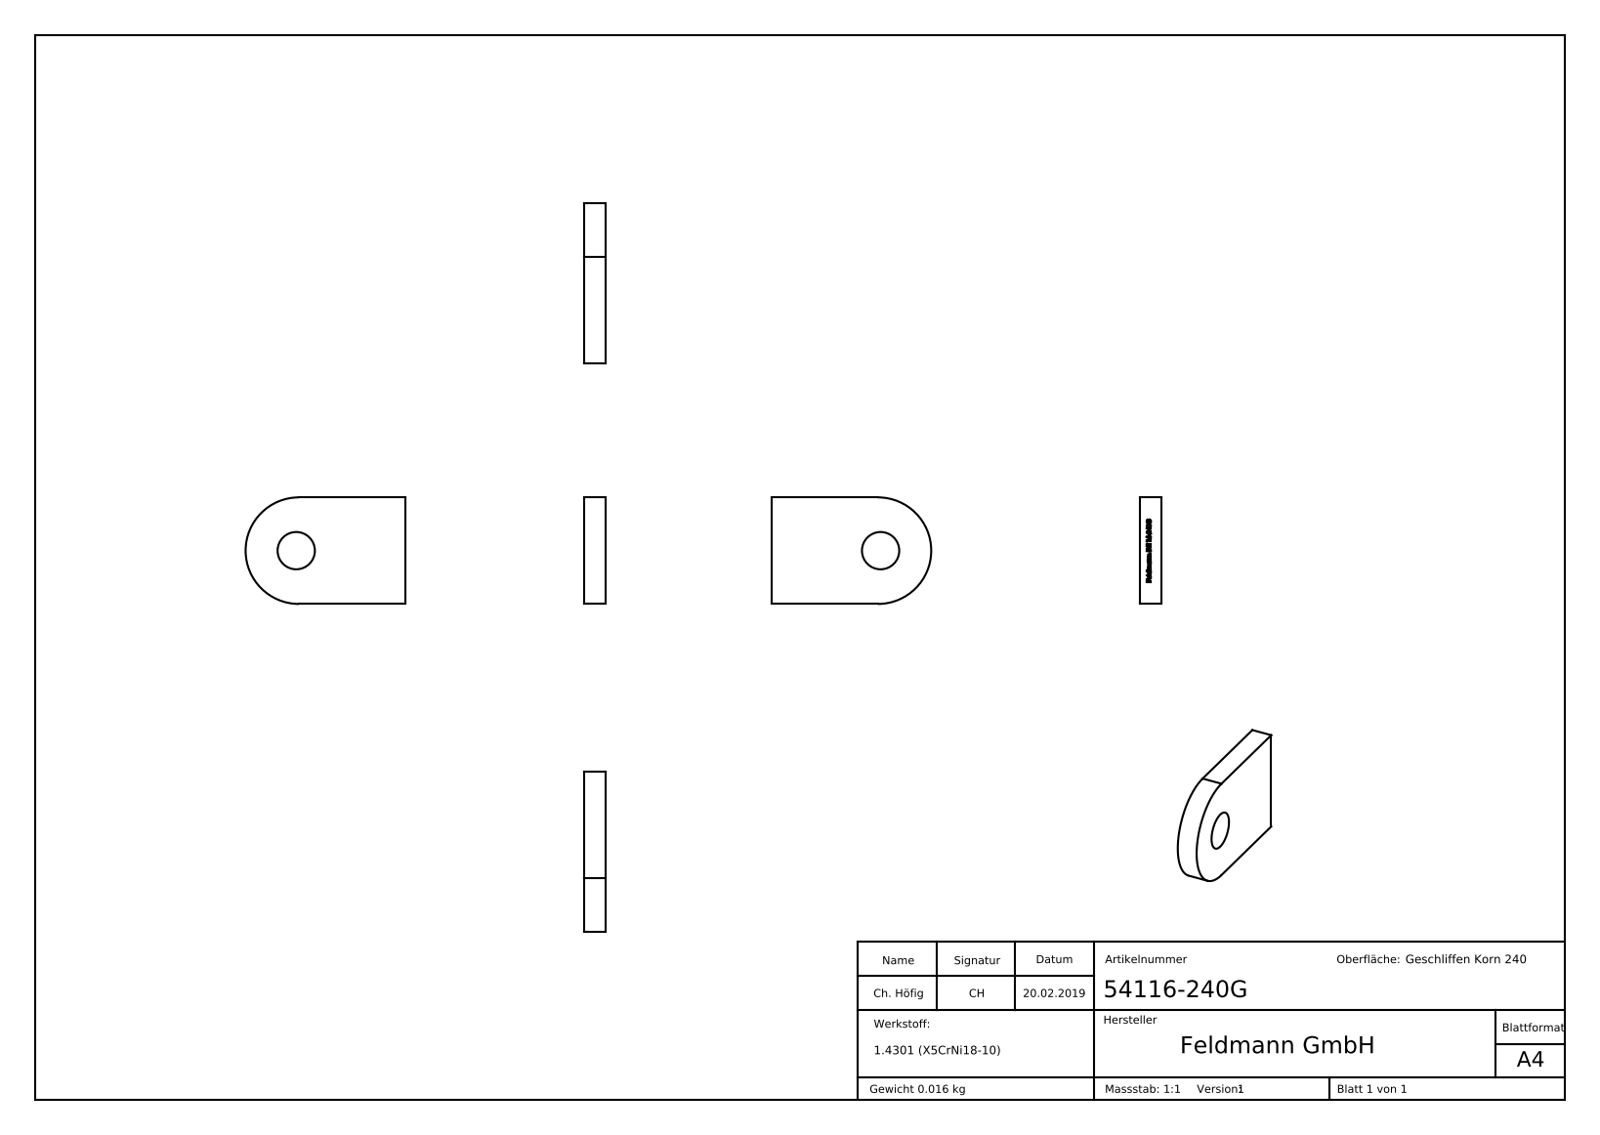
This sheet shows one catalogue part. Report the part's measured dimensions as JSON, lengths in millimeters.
{"part_name": "54116-240G", "step_written_by": "SolidWorks 2015 (CONFIG_CONTROL_DESIGN)", "units": "millimeters", "bodies": {"solids": 1, "faces": 238, "planar": 145, "cylindrical": 4, "other": 89}, "overall_size": [30, 20, 4], "volume_mm3": 2074, "surface_area_mm2": 1497, "round_holes": [[7, 1]], "partial_cylinders_radius": [[10, 1]], "face_to_face_distances": [4, 20, 2, 0.61, 0.53, 2.82, 1.21, 1.29, 0.48, 6.44]}
